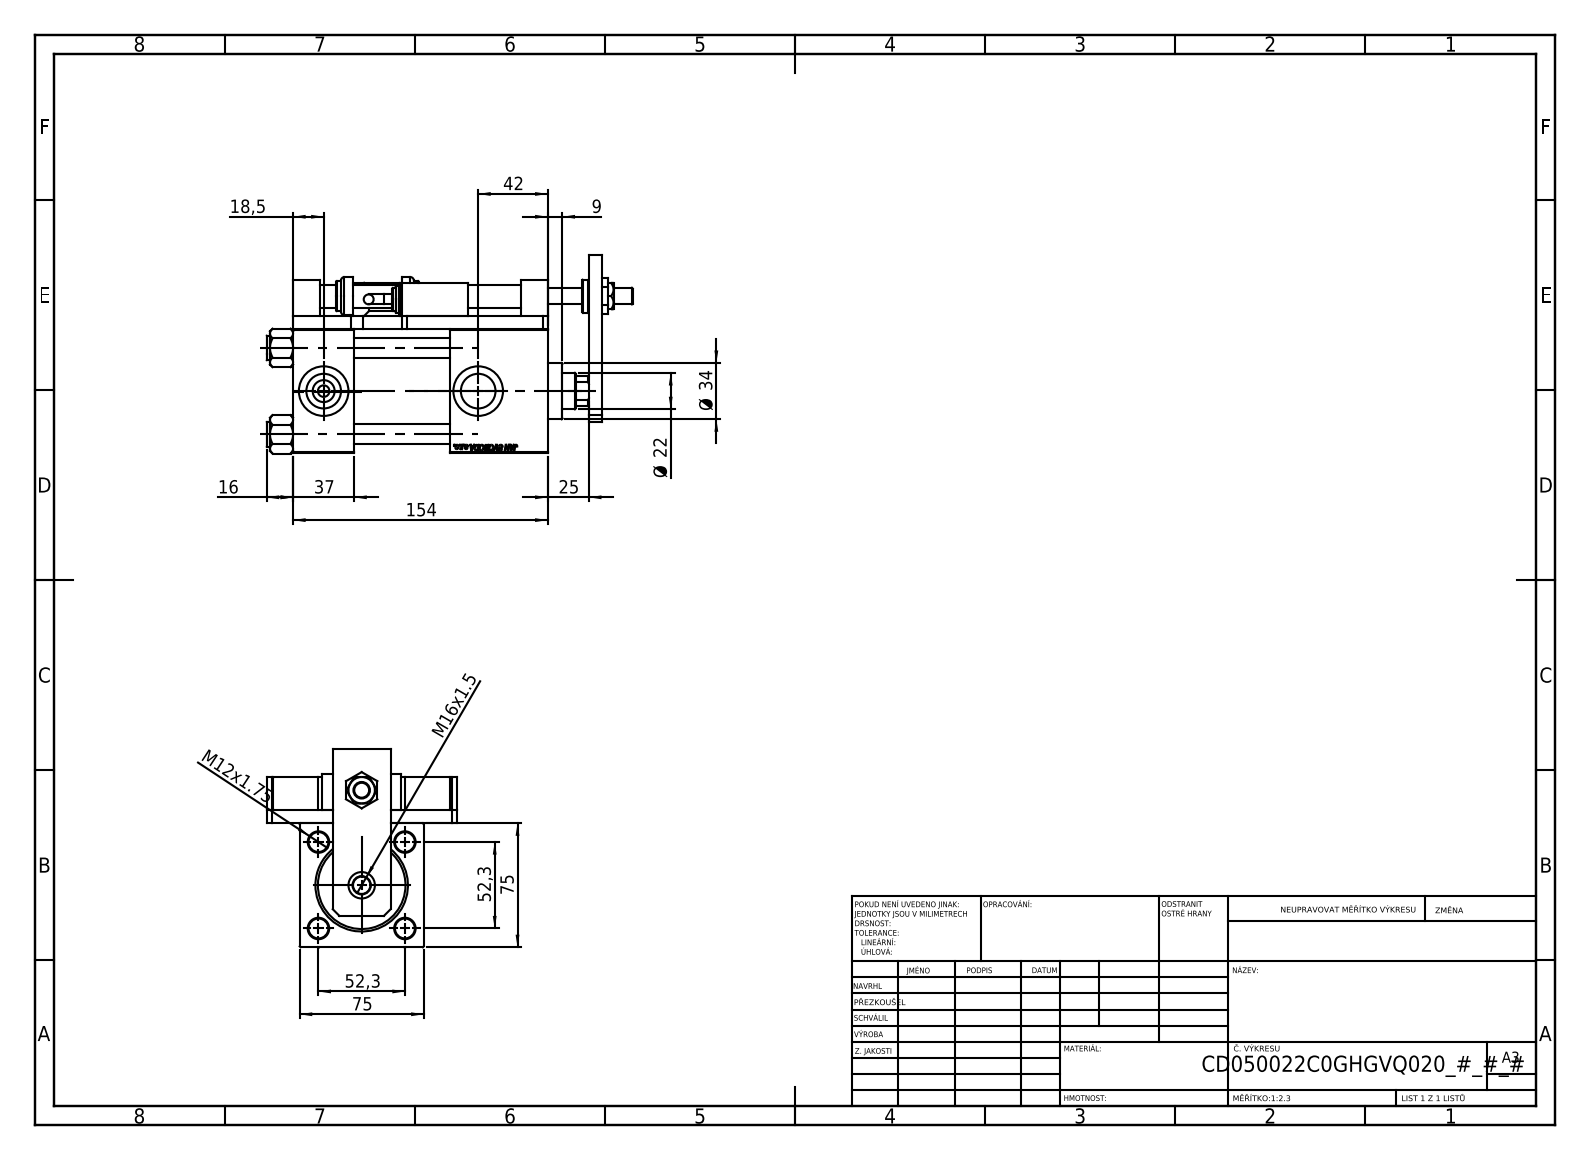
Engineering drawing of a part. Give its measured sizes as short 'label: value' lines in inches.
name: V215CD_C_TYCINKA; V215CD_SWITCH_Q_SWITCH; V215CD_SWITCH_Q_PODLOZKA_FRONT; V215CD_SWITCH_Q_PODLOZKA_BACK (+7 more)
written by: SolidWorks 2019 (CONFIG_CONTROL_DESIGN)
unit: in
bodies: 24 solids, 1376 faces (647 planar, 154 cylindrical, 575 other)
size: 8.72 × 4.735 × 4.528
volume: 55.84 in³; area: 356.9 in²
holes: 4× ⌀0.335, 4× ⌀0.472, 4× ⌀0.531, 2× ⌀0.276, 2× ⌀0.825, 2× ⌀1.181, 1× ⌀0.394, 1× ⌀0.413, 1× ⌀0.551, 1× ⌀0.63, 1× ⌀0.866, 1× ⌀0.984
bosses: 4× ⌀0.591, 3× ⌀0.787, 2× ⌀0.63, 2× ⌀0.551, 2× ⌀0.236, 1× ⌀2.205, 1× ⌀1.339, 1× ⌀0.906
rounds: 4× R0.295, 1× R0.413
face distances: 0.315, 2.953, 0.787, 1.457, 3.268, 3.74, 6.063, 4.606, 3.622, 2.323
hole spacings: 1.456, 2.059, 1.26, 1.607, 2.912, 3.45, 5.433, 5.577
